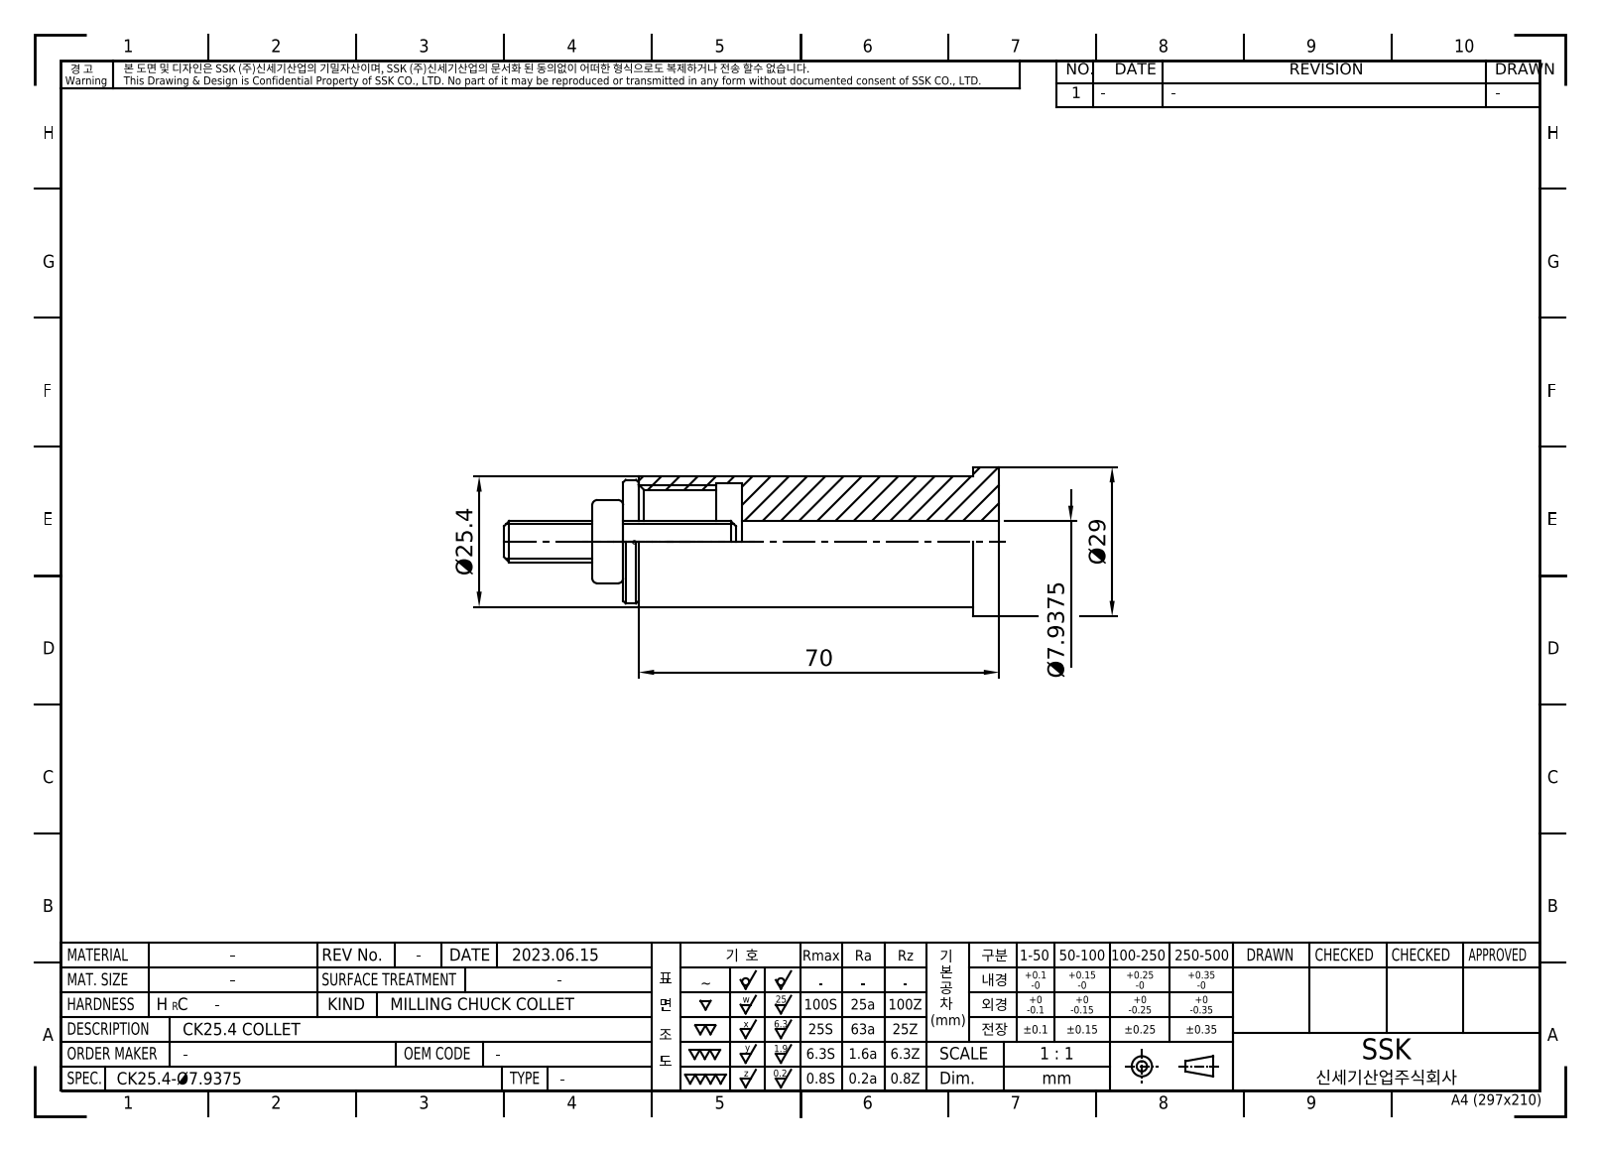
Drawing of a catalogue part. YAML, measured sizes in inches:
part_name: "LO-CK19.05-7.9375"
step_written_by: "Autodesk Inventor 2022 (AUTOMOTIVE_DESIGN)"
units: inches
bodies: {solids: 1, faces: 10, planar: 5, cylindrical: 5, other: 0}
overall_size: [2.756, 1.142, 1.142]
volume: 1.625
surface_area: 14.81
round_holes:
  - {diameter: 0.313, count: 1}
  - {diameter: 0.824, count: 1}
  - {diameter: 0.886, count: 1}
round_bosses_or_shafts:
  - {diameter: 1.142, count: 1}
  - {diameter: 1, count: 1}
face_to_face_distances: [1.969, 0.197, 0.787, 2.756, 2.559, 1.772, 0.591, 2.165]
